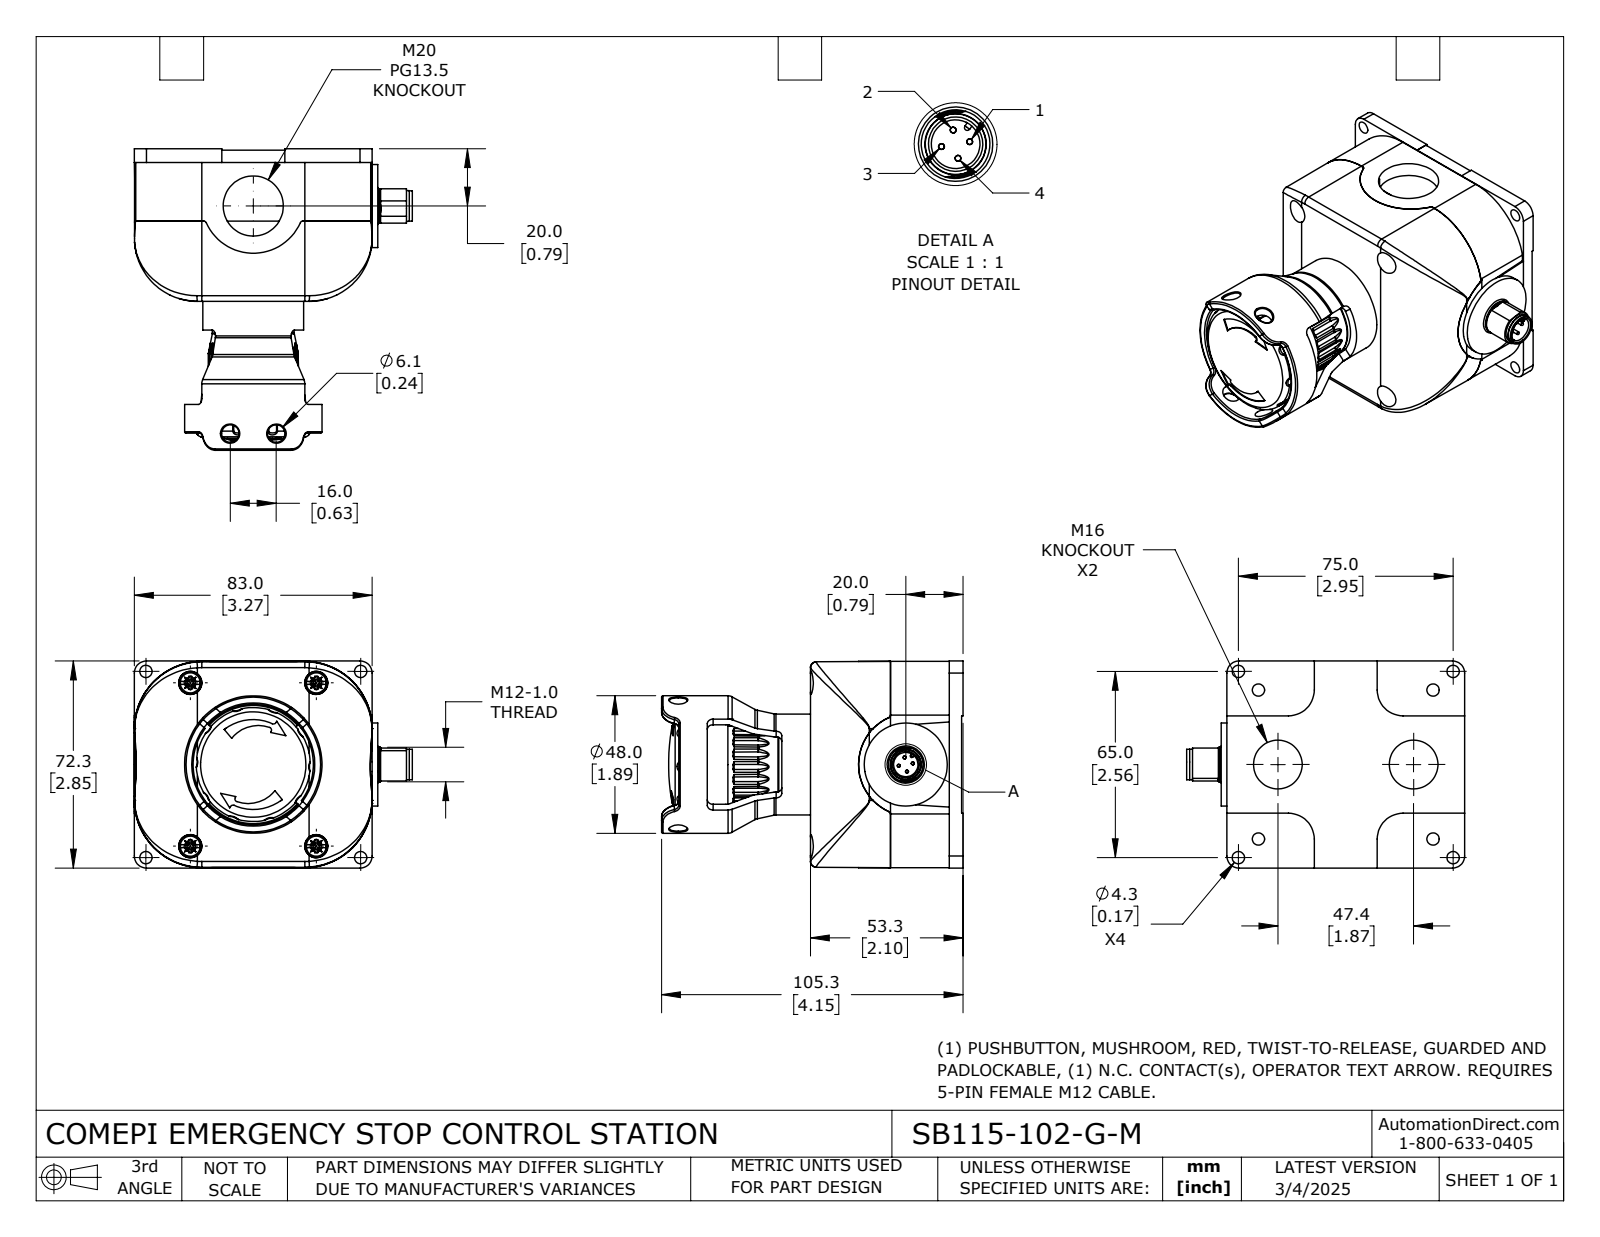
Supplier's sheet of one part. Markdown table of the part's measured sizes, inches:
| quantity | value |
| --- | --- |
| part name | SB115-102-G-M |
| STEP written by | SolidWorks 2024 (CONFIG_CONTROL_DESIGN) |
| units | inches |
| bodies | 7 solids, 1233 faces (436 planar, 345 cylindrical, 452 other) |
| overall size | 4.146 × 3.821 × 2.846 |
| volume | 15.56 in³ |
| surface area | 128.9 in² |
| round holes (diameter × count) | 0.169 × 8, 0.039 × 4, 0.04 × 4, 0.067 × 4, 0.087 × 4, 0.323 × 4, 0.24 × 2, 0.669 × 2, 0.827 × 2, 0.051 × 1, 0.335 × 1, 0.713 × 1 |
| round bosses / shafts (diameter × count) | 0.276 × 4, 0.085 × 4, 0.065 × 4, 1.142 × 2, 0.024 × 2, 1.89 × 1, 1.386 × 1, 1.039 × 1 |
| partial cylindrical surfaces (radius × count) | 0.039 × 28, 0.079 × 16, 0.268 × 10, 0.02 × 5, 0.035 × 4, 0.236 × 4, 0.354 × 4, 0.38 × 4 |
| main face-to-face distances | 0.976, 0.098, 0.878, 2.079, 1.98, 1.102, 0.02, 0.118, 0.996, 2.098 |
| hole center spacings | 0.376, 1.058, 1.39, 1.578, 1.954, 2.32, 2.367, 2.689 |
